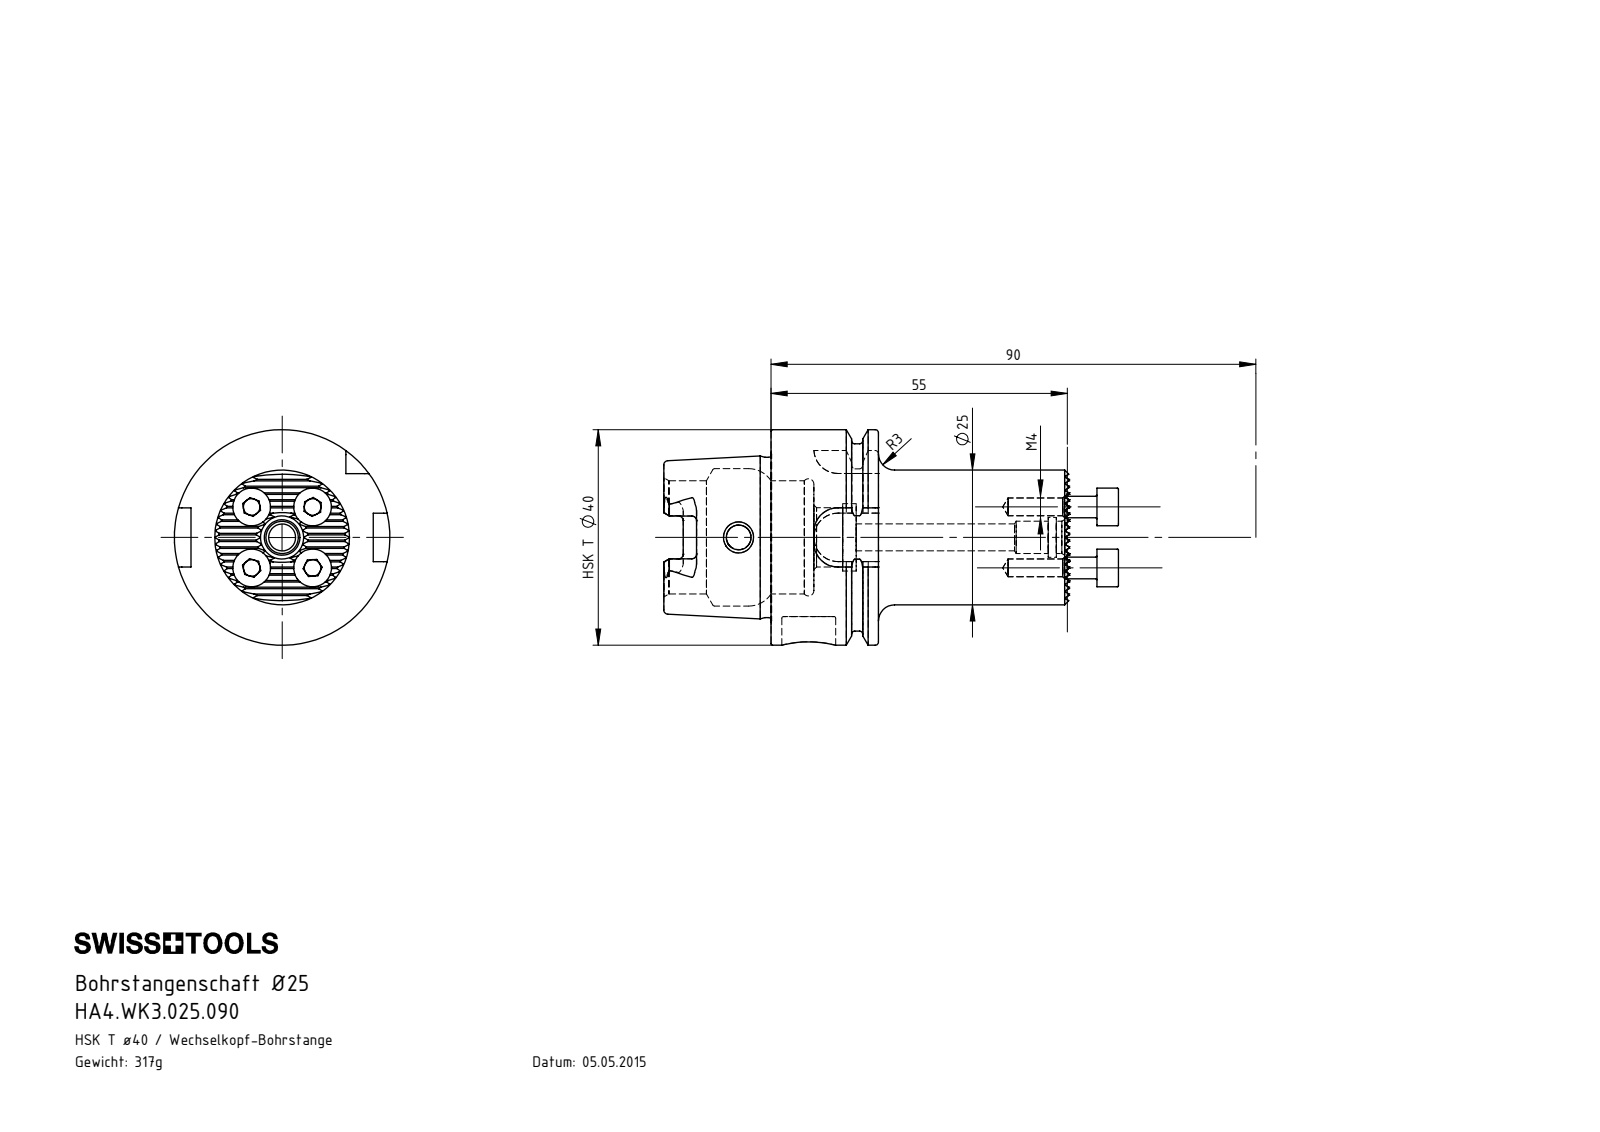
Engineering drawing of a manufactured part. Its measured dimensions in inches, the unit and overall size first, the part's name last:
Units: inches
Overall size (bounding box): 3.323 × 1.575 × 1.575
Round holes (diameter × count): ⌀0.13 ×4, ⌀0.181 ×1, ⌀0.197 ×1, ⌀0.236 ×1, ⌀0.291 ×1, ⌀0.394 ×1, ⌀0.433 ×1, ⌀0.492 ×1, ⌀0.827 ×1, ⌀1.004 ×1
Round bosses / shafts (diameter × count): ⌀0.276 ×3, ⌀0.157 ×3, ⌀1.575 ×1, ⌀1.368 ×1, ⌀1.17 ×1, ⌀0.984 ×1
Partial cylindrical surfaces — rounded edges, fillets, slot ends (radius × count): R0.005 ×19, R0.035 ×6, R0.074 ×4, R0.177 ×4
Main face-to-face distances: 0.785, 0.17, 0.043, 0.472, 0.128, 0.341, 0.313, 0.213, 0.298, 0.085
Hole centre spacings: 0.315, 0.446, 0.63
Volume: 2.506 in³ · Surface area: 22.49 in²
Bodies: 5 solids, 448 faces (221 planar, 114 cylindrical, 113 other)
Part name (STEP PRODUCT): HA4.WK3.025.090; HA4-WK3.025.090_A; ISO 4762 - M4 x 12; DIN 3771 - 6x1
STEP written by: SolidWorks 2017 (AUTOMOTIVE_DESIGN)
